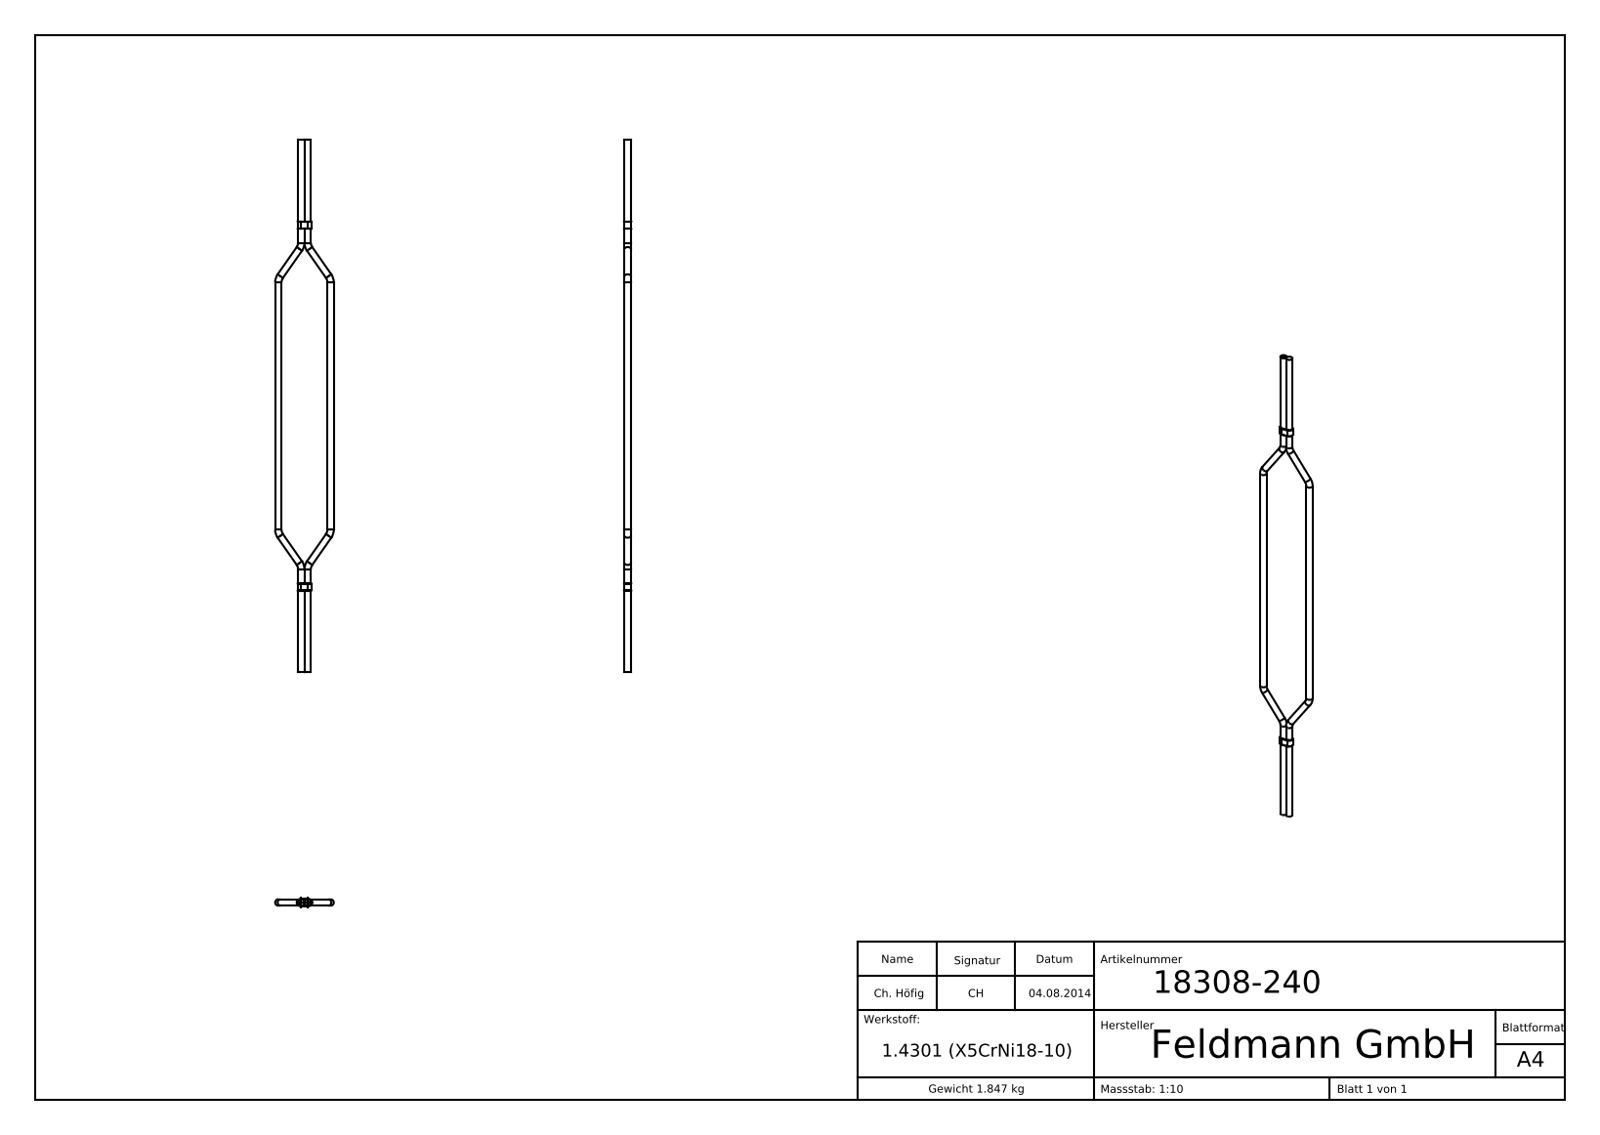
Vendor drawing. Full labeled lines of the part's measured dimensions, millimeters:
Part name (STEP PRODUCT): 18308-240
STEP written by: SolidWorks 2015 (CONFIG_CONTROL_DESIGN)
Units: millimetres
Bodies: 4 solids, 185 faces (77 planar, 36 cylindrical, 72 other)
Overall size (bounding box): 1000 × 110 × 14.1
Volume: 233 740 mm³ · Surface area: 81 586 mm²
Round bosses / shafts (diameter × count): ⌀12 ×8
Partial cylindrical surfaces — rounded edges, fillets, slot ends (radius × count): R1 ×8, R6.05 ×3, R7.05 ×3
Main face-to-face distances: 1, 13.1, 12.1, 14.1, 1000, 1.78, 999.5, 0.5, 0.44, 0.67
